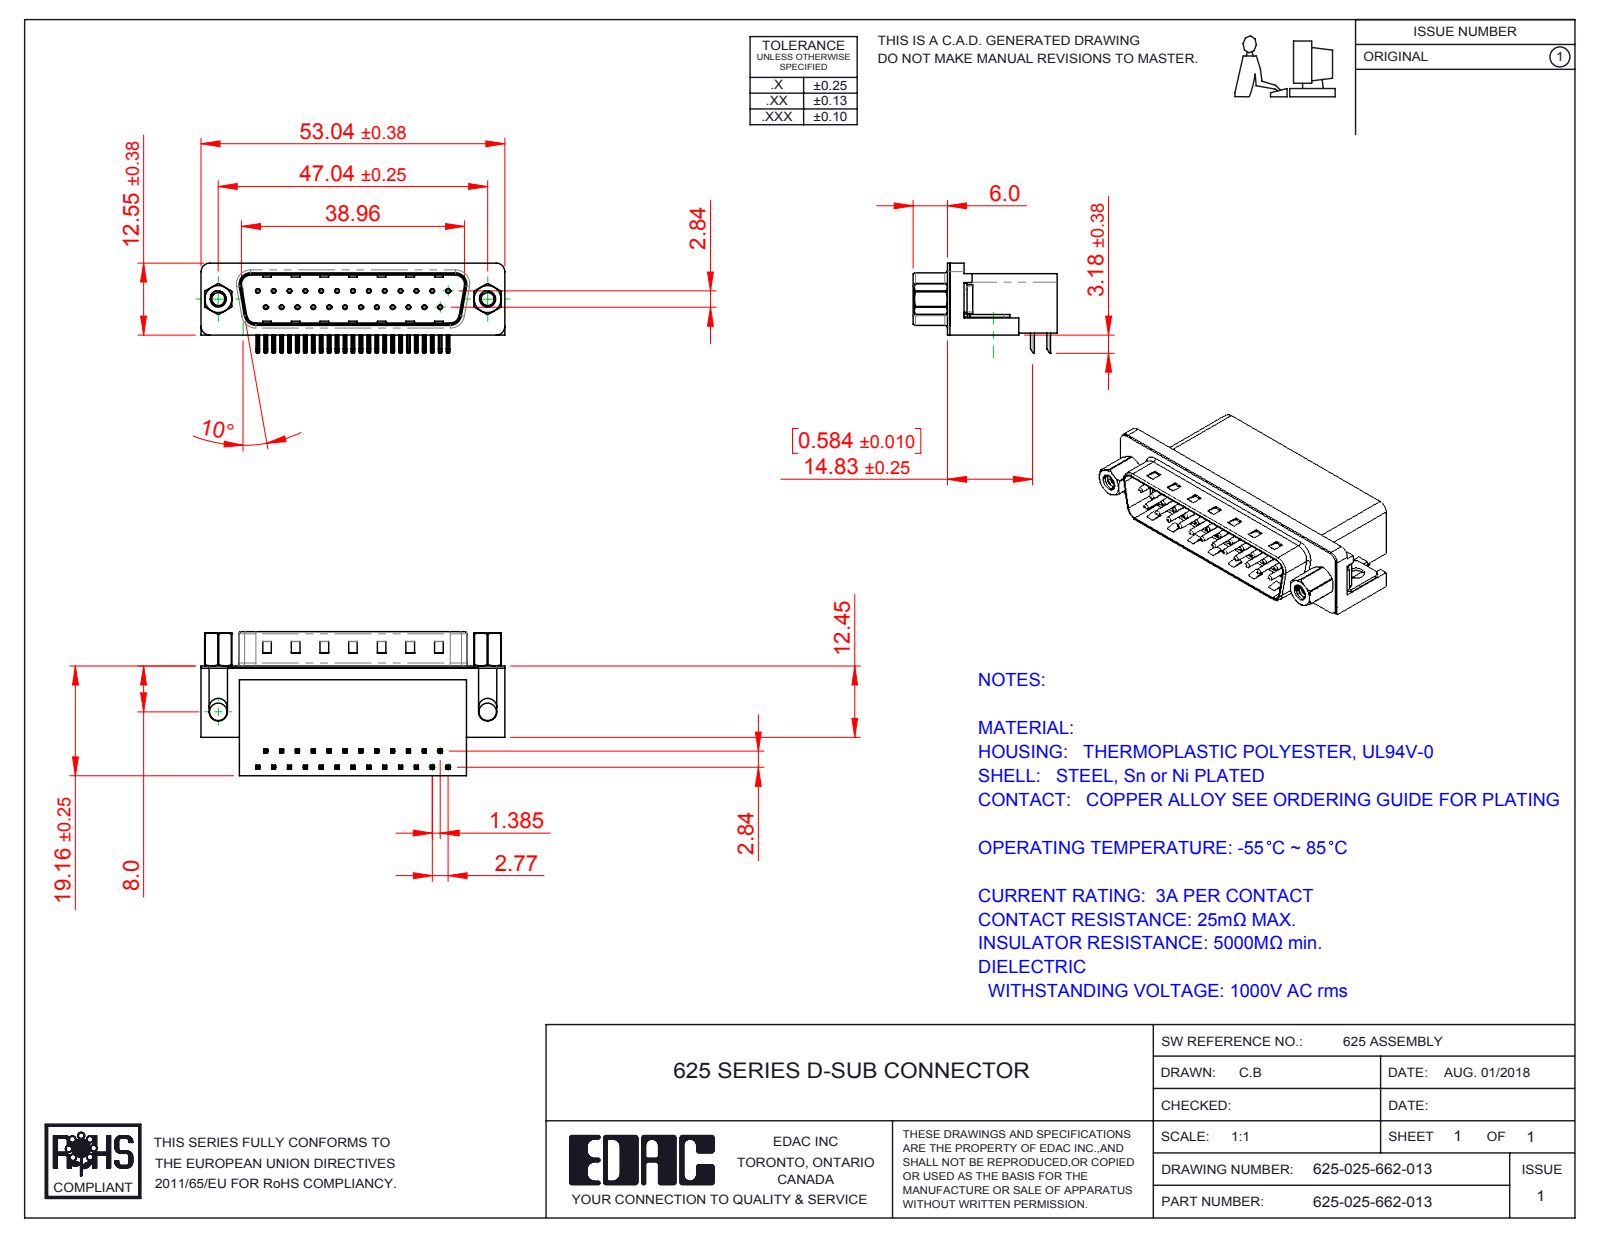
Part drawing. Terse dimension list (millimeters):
name: 625 Contact Bottom; 625 Housing_25 Socket; 625 4-40 Hex Standoff 5; 625 Thru Hole Board Mount (+4 more)
written by: SolidWorks 2016 (CONFIG_CONTROL_DESIGN)
unit: mm
bodies: 33 solids, 2391 faces (1427 planar, 733 cylindrical, 231 other)
size: 53.04 × 25.16 × 15.73
volume: 9 375 mm³; area: 9 332 mm²
holes: 25× ⌀0.35, 25× ⌀0.8, 2× ⌀2.26, 2× ⌀2.29, 2× ⌀3.05, 2× ⌀4, 2× ⌀4.8, 2× ⌀5
bosses: 25× ⌀0.75, 2× ⌀4.9, 2× ⌀4.75, 2× ⌀3.9, 2× ⌀2.79
rounds: 108× R0.25, 50× R0.12, 16× R1, 9× R0.5, 8× R1.6, 7× R1.5, 4× R0.9, 4× R2
face distances: 0.4, 10.35, 18.76, 2.1, 8.76, 10.46, 10.86, 1.7, 19.16, 10.11
hole spacings: 3.16, 2.77, 11.08, 5.54, 8.31, 5.03, 13.85, 7.48
